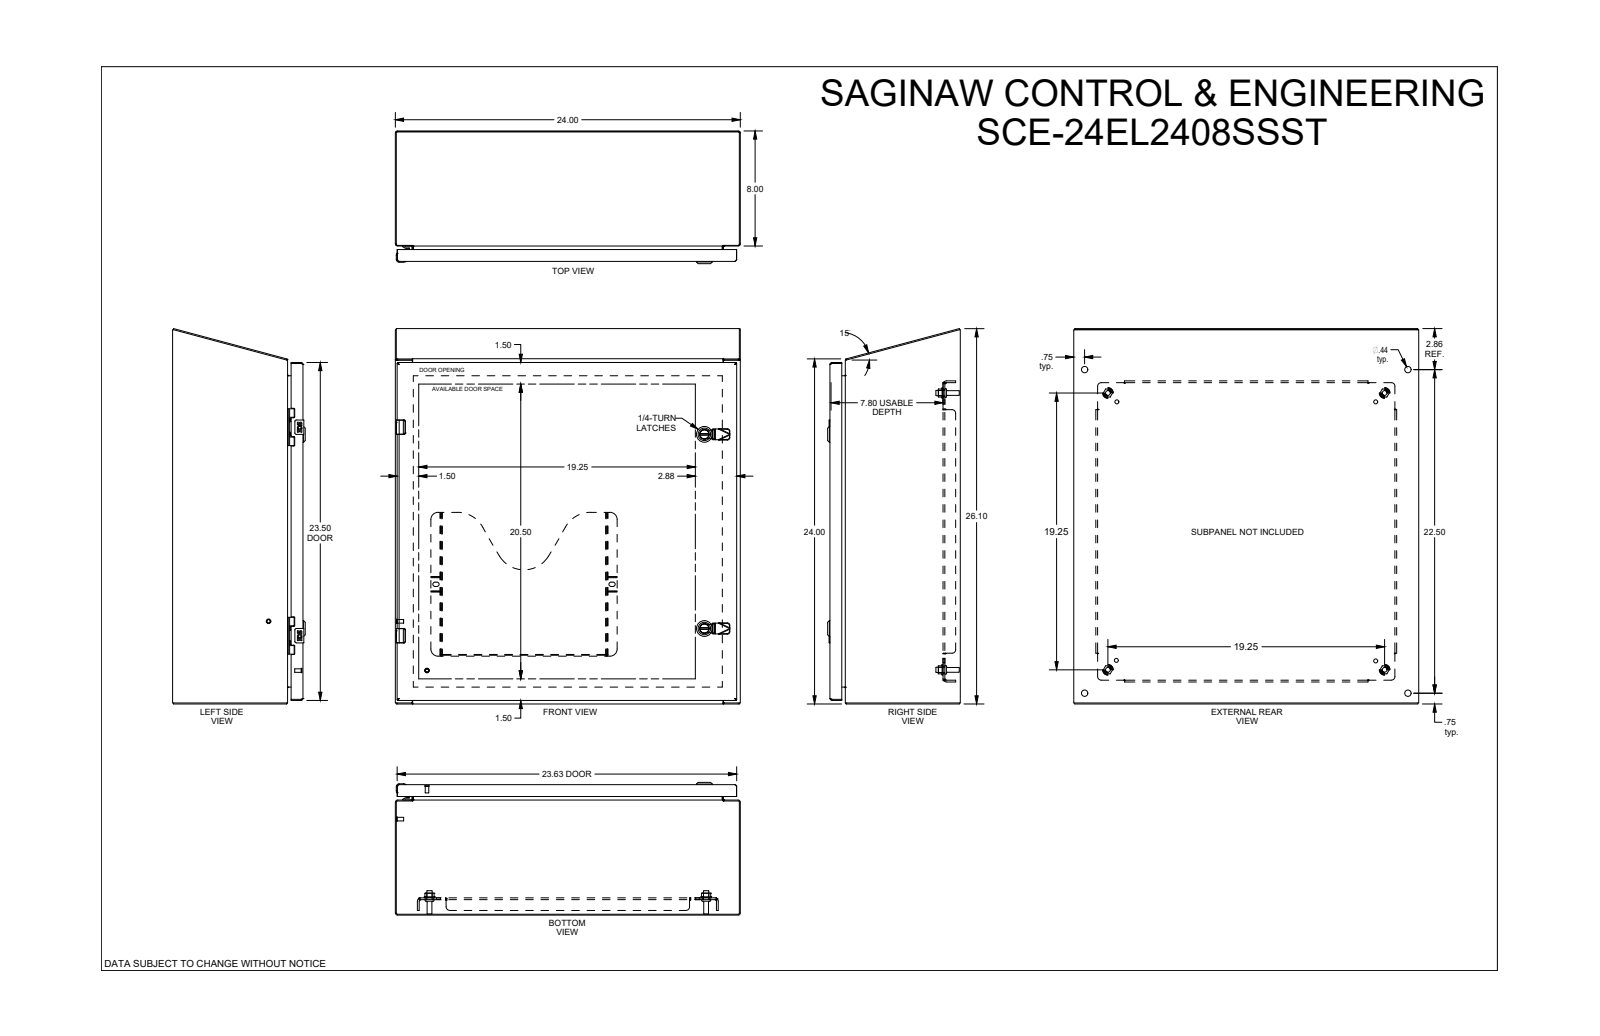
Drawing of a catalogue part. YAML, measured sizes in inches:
part_name: "SCE-24EL2408SSST"
step_written_by: "SolidWorks 2019 (CONFIG_CONTROL_DESIGN)"
units: inches
bodies: {solids: 0, faces: 2844, planar: 1311, cylindrical: 759, other: 774}
overall_size: [26.106, 24, 9.23]
round_holes:
  - {diameter: 0.172, count: 4}
  - {diameter: 0.205, count: 4}
  - {diameter: 0.244, count: 4}
  - {diameter: 0.266, count: 4}
  - {diameter: 0.281, count: 4}
  - {diameter: 0.367, count: 4}
  - {diameter: 0.375, count: 4}
  - {diameter: 0.437, count: 4}
  - {diameter: 0.5, count: 4}
  - {diameter: 0.156, count: 2}
  - {diameter: 0.197, count: 2}
  - {diameter: 0.218, count: 2}
round_bosses_or_shafts:
  - {diameter: 0.17, count: 6}
  - {diameter: 0.366, count: 4}
  - {diameter: 0.332, count: 4}
  - {diameter: 0.25, count: 4}
  - {diameter: 0.248, count: 4}
  - {diameter: 0.196, count: 3}
  - {diameter: 1.102, count: 2}
  - {diameter: 0.866, count: 2}
partial_cylinders:
  - {radius: 0.012, count: 56}
  - {radius: 0.015, count: 32}
  - {radius: 0.01, count: 28}
  - {radius: 0.04, count: 23}
  - {radius: 0.02, count: 20}
  - {radius: 0.029, count: 12}
  - {radius: 0.06, count: 11}
  - {radius: 0.07, count: 10}
face_to_face_distances: [0.075, 0.075, 8.998, 8.923, 9.073, 8.998, 1.2, 7.873, 1, 0.125]
hole_center_spacings: [14.5, 0.985, 20.38, 0.02, 2.298, 4.493, 20.938, 20.938]
